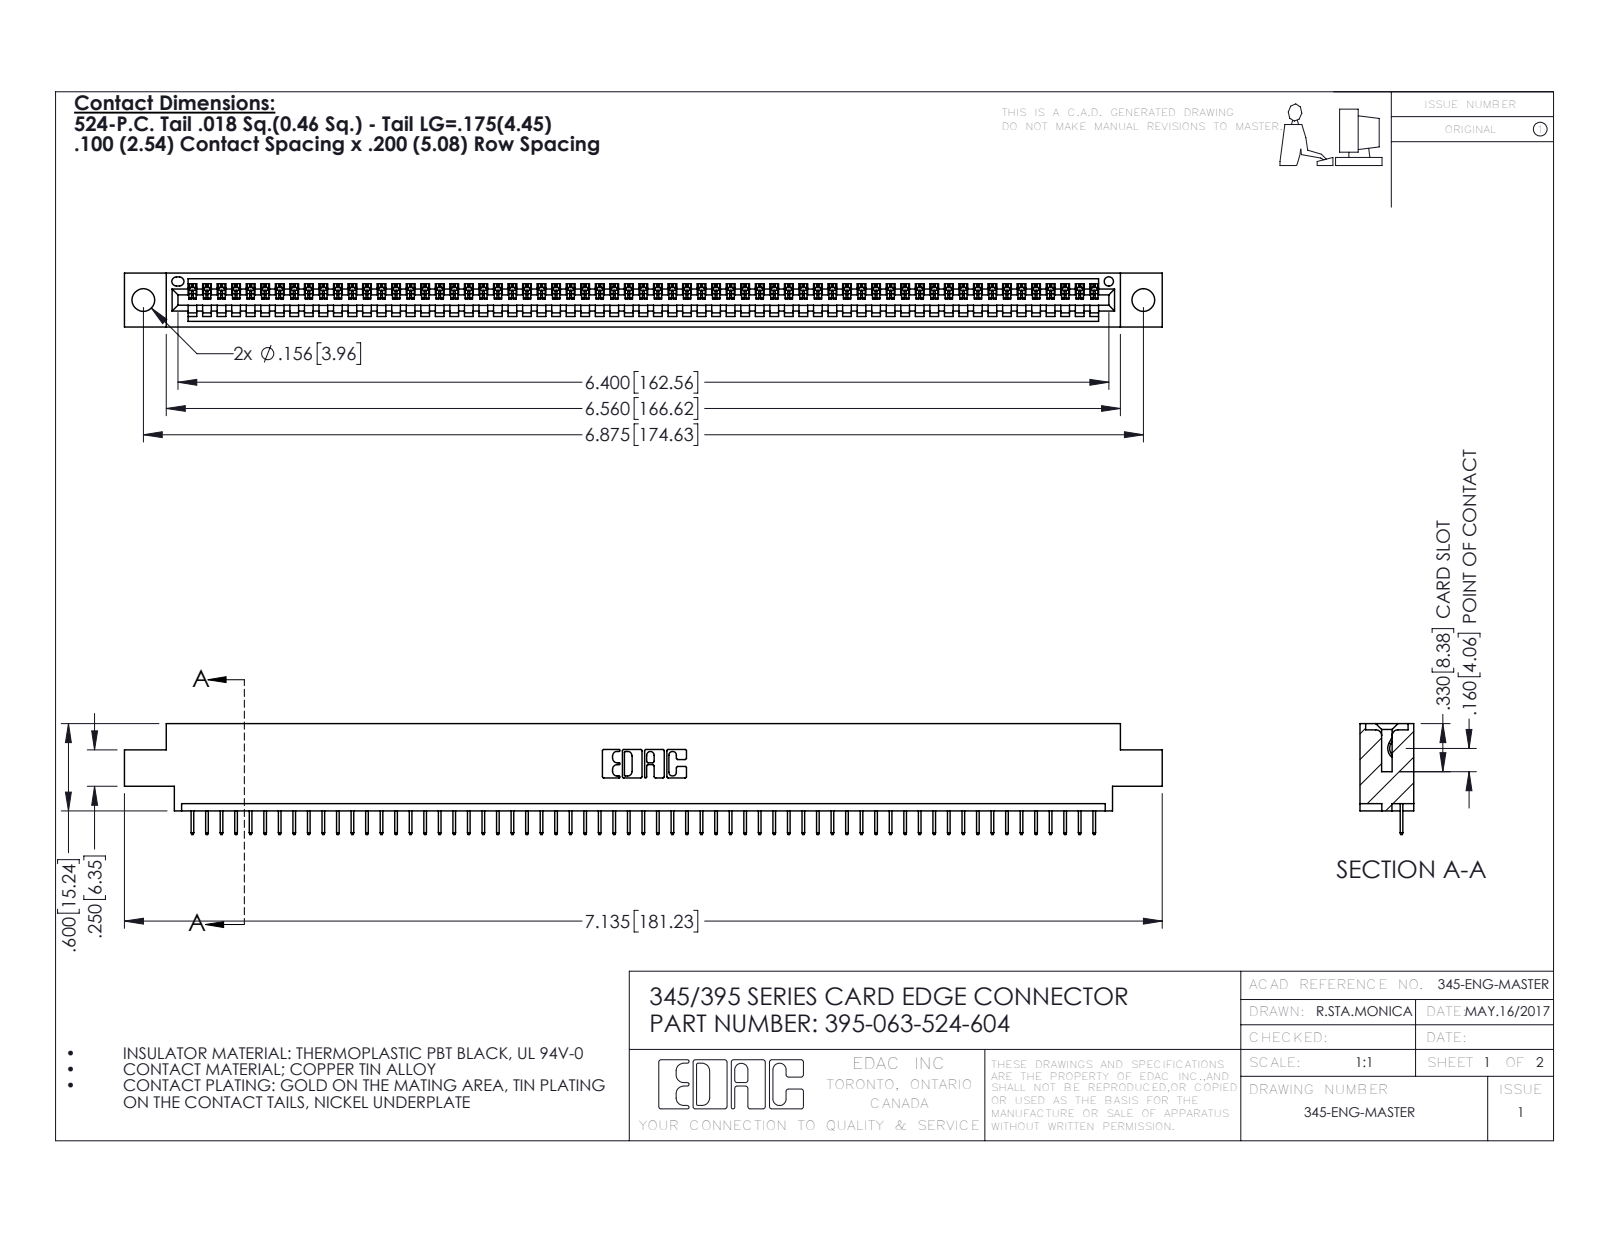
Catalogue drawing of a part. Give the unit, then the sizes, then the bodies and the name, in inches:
Units: inches
Overall size (bounding box): 7.135 × 0.762 × 0.37
Round holes (diameter × count): ⌀0.156 ×2, ⌀0.064 ×1
Partial cylindrical surfaces — rounded edges, fillets, slot ends (radius × count): R0.006 ×126, R0.01 ×22, R0.007 ×6, R0.031 ×6, R0.026 ×3, R0.031 ×2, R0.04 ×2, R0.014 ×1
Main face-to-face distances: 0.072, 0.298, 0.37, 0.2, 0.098, 0.272, 0.025, 0.225, 0.072, 0.175
Hole centre spacings: 0.27, 6.639, 6.875
Volume: 1.033 in³ · Surface area: 33.99 in²
Bodies: 64 solids, 4036 faces (2982 planar, 1054 cylindrical, 0 other)
Part name (STEP PRODUCT): 345 Part_0.170 Offset - 0.156 Dia-TH; 345-292-001_345-293-124; 395-063-524-604
STEP written by: SolidWorks 2016 (CONFIG_CONTROL_DESIGN)
